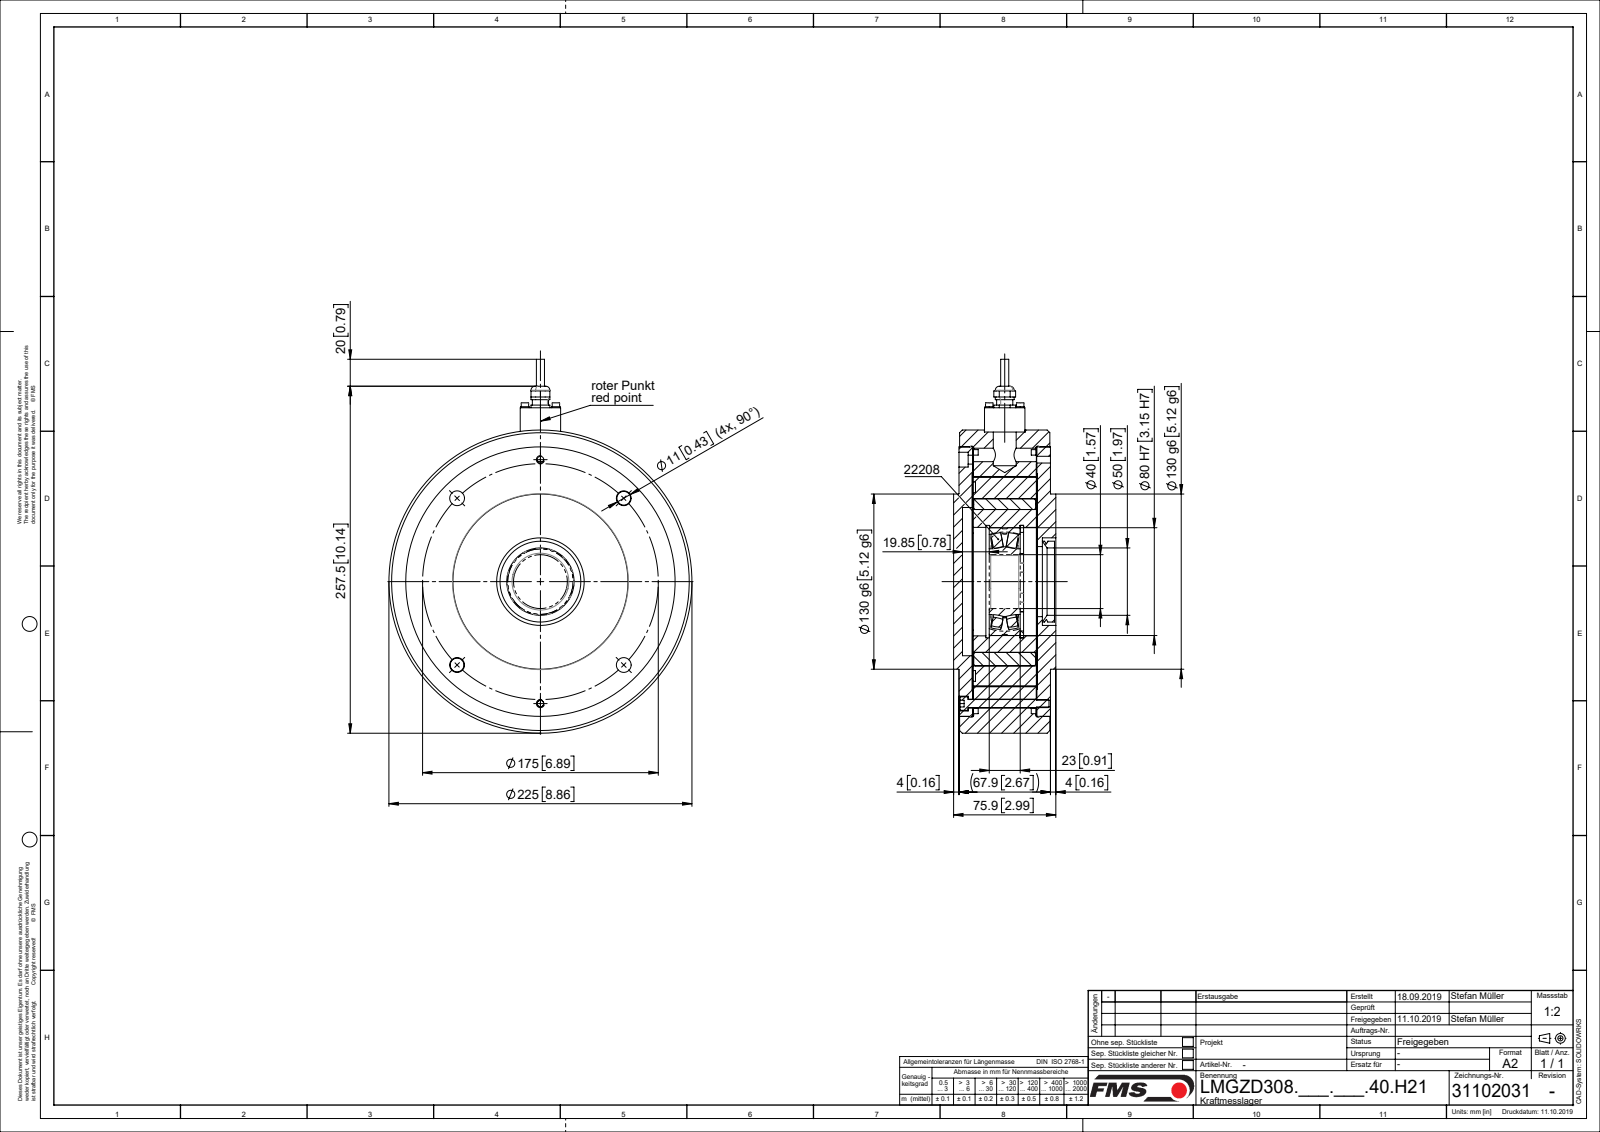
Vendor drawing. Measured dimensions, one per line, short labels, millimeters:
name: 31102024_01; 43404.02_01; 49083_01; Steuerkabel_6x20 (+8 more)
written by: SolidWorks 2018 (CONFIG_CONTROL_DESIGN)
unit: mm
bodies: 53 solids, 762 faces (220 planar, 271 cylindrical, 271 other)
size: 277.5 × 225 × 75.9
volume: 2 375 000 mm³; area: 443 519 mm²
holes: 6× ⌀11, 4× ⌀2.5, 4× ⌀3.1, 4× ⌀3.4, 3× ⌀3.2, 2× ⌀3, 2× ⌀5, 2× ⌀6.6, 2× ⌀10, 2× ⌀10.2, 1× ⌀6, 1× ⌀8
bosses: 4× ⌀6.2, 4× ⌀5.5, 4× ⌀3, 1× ⌀225, 1× ⌀199, 1× ⌀188, 1× ⌀132, 1× ⌀130
rounds: 4× R0.1, 4× R11, 2× R4.91, 1× R33.25, 1× R79, 1× R82, 1× R86
face distances: 47.25, 10.2, 10.45, 57.45, 57.7, 0.5, 0.75, 47.75, 48, 9.7
hole spacings: 16.26, 23, 62.02, 68.17, 87.5, 123.74, 134.45, 164.45
